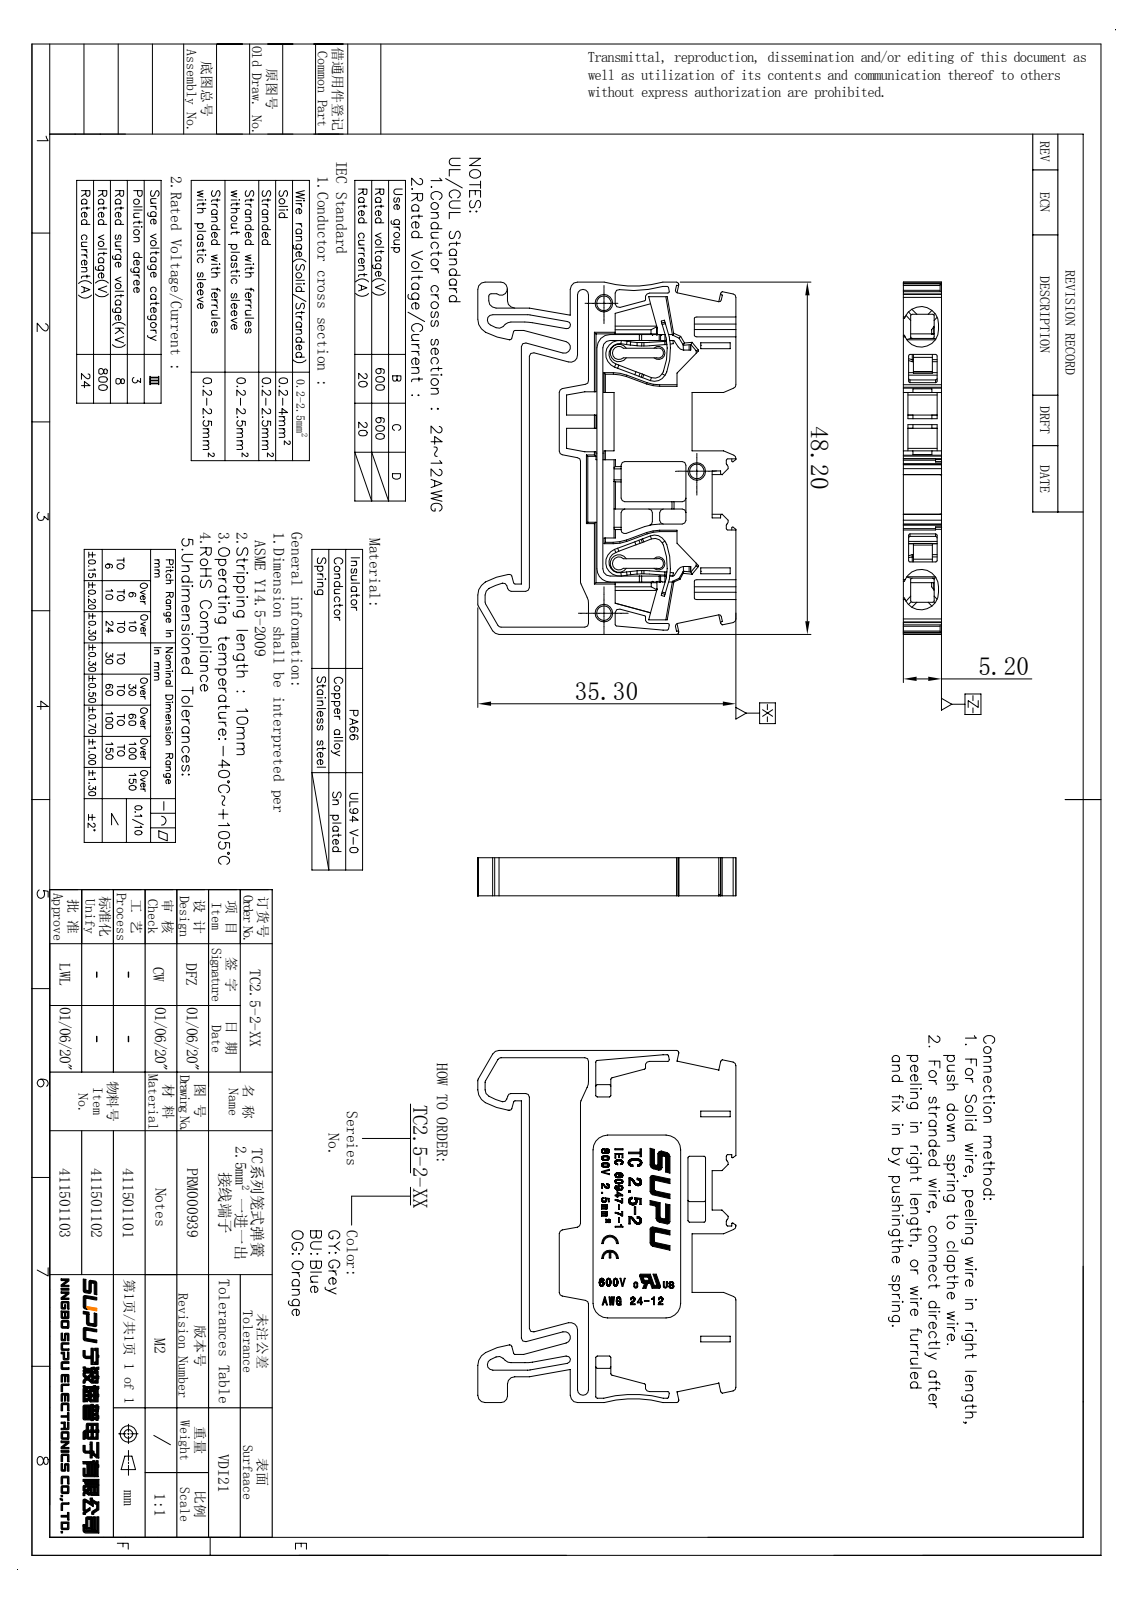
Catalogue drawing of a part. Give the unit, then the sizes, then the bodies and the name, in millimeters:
Units: millimetres
Overall size (bounding box): 48.2 × 35.3 × 5.2
Partial cylindrical surfaces — rounded edges, fillets, slot ends (radius × count): R0.2 ×23, R0.5 ×21, R0.3 ×9, R1 ×7, R0.15 ×6, R2 ×4, R2.4 ×4, R3 ×4
Main face-to-face distances: 5.2, 3.2, 2, 1.2, 1.1, 0.6, 8.1, 1, 1.4, 2.6
Volume: 5 338 mm³ · Surface area: 4 877 mm²
Bodies: 34 solids, 2555 faces (2403 planar, 116 cylindrical, 36 other)
Part name (STEP PRODUCT): SP6101T1000-04
STEP written by: SIEMENS PLM Software NX 12.0 (AUTOMOTIVE_DESIGN)
